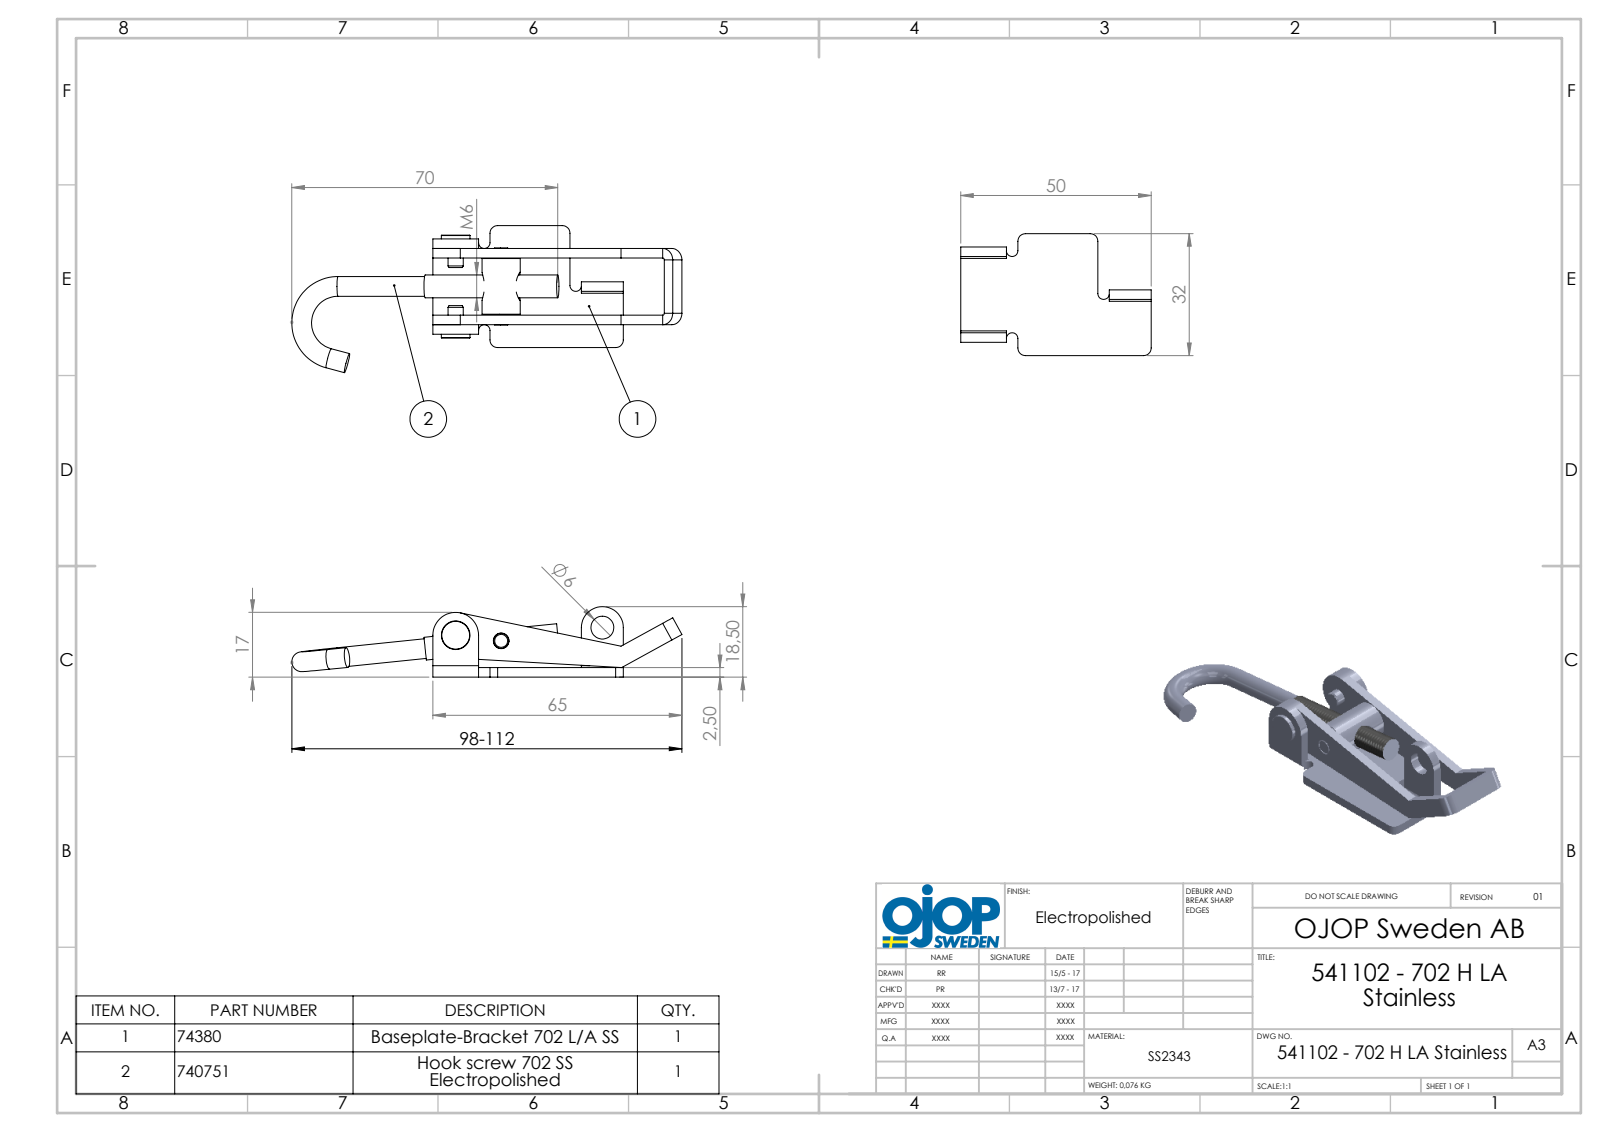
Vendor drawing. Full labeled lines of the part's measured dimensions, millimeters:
Part name (STEP PRODUCT): 702 - Ansatsnit; 702 - Bygel; 702 - Rulle; 702 - Platta LA (+2 more)
STEP written by: SolidWorks 2015 (AUTOMOTIVE_DESIGN)
Units: millimetres
Bodies: 6 solids, 147 faces (65 planar, 64 cylindrical, 18 other)
Overall size (bounding box): 105.89 × 38.54 × 18.5
Volume: 10 286 mm³ · Surface area: 9 902 mm²
Round holes (diameter × count): ⌀4.1 ×2, ⌀6 ×2, ⌀5 ×1
Round bosses / shafts (diameter × count): ⌀5.18 ×2, ⌀4 ×2, ⌀10 ×1, ⌀7.5 ×1, ⌀6 ×1
Partial cylindrical surfaces — rounded edges, fillets, slot ends (radius × count): R0.5 ×5, R3 ×5, R2 ×4, R1.5 ×2, R1.51 ×1, R5.5 ×1, R6 ×1
Main face-to-face distances: 2.5, 17.5, 20, 8.75, 11.25, 15, 5, 6.25, 22.5, 6
Hole centre spacings: 12.02, 26.8, 38.55
